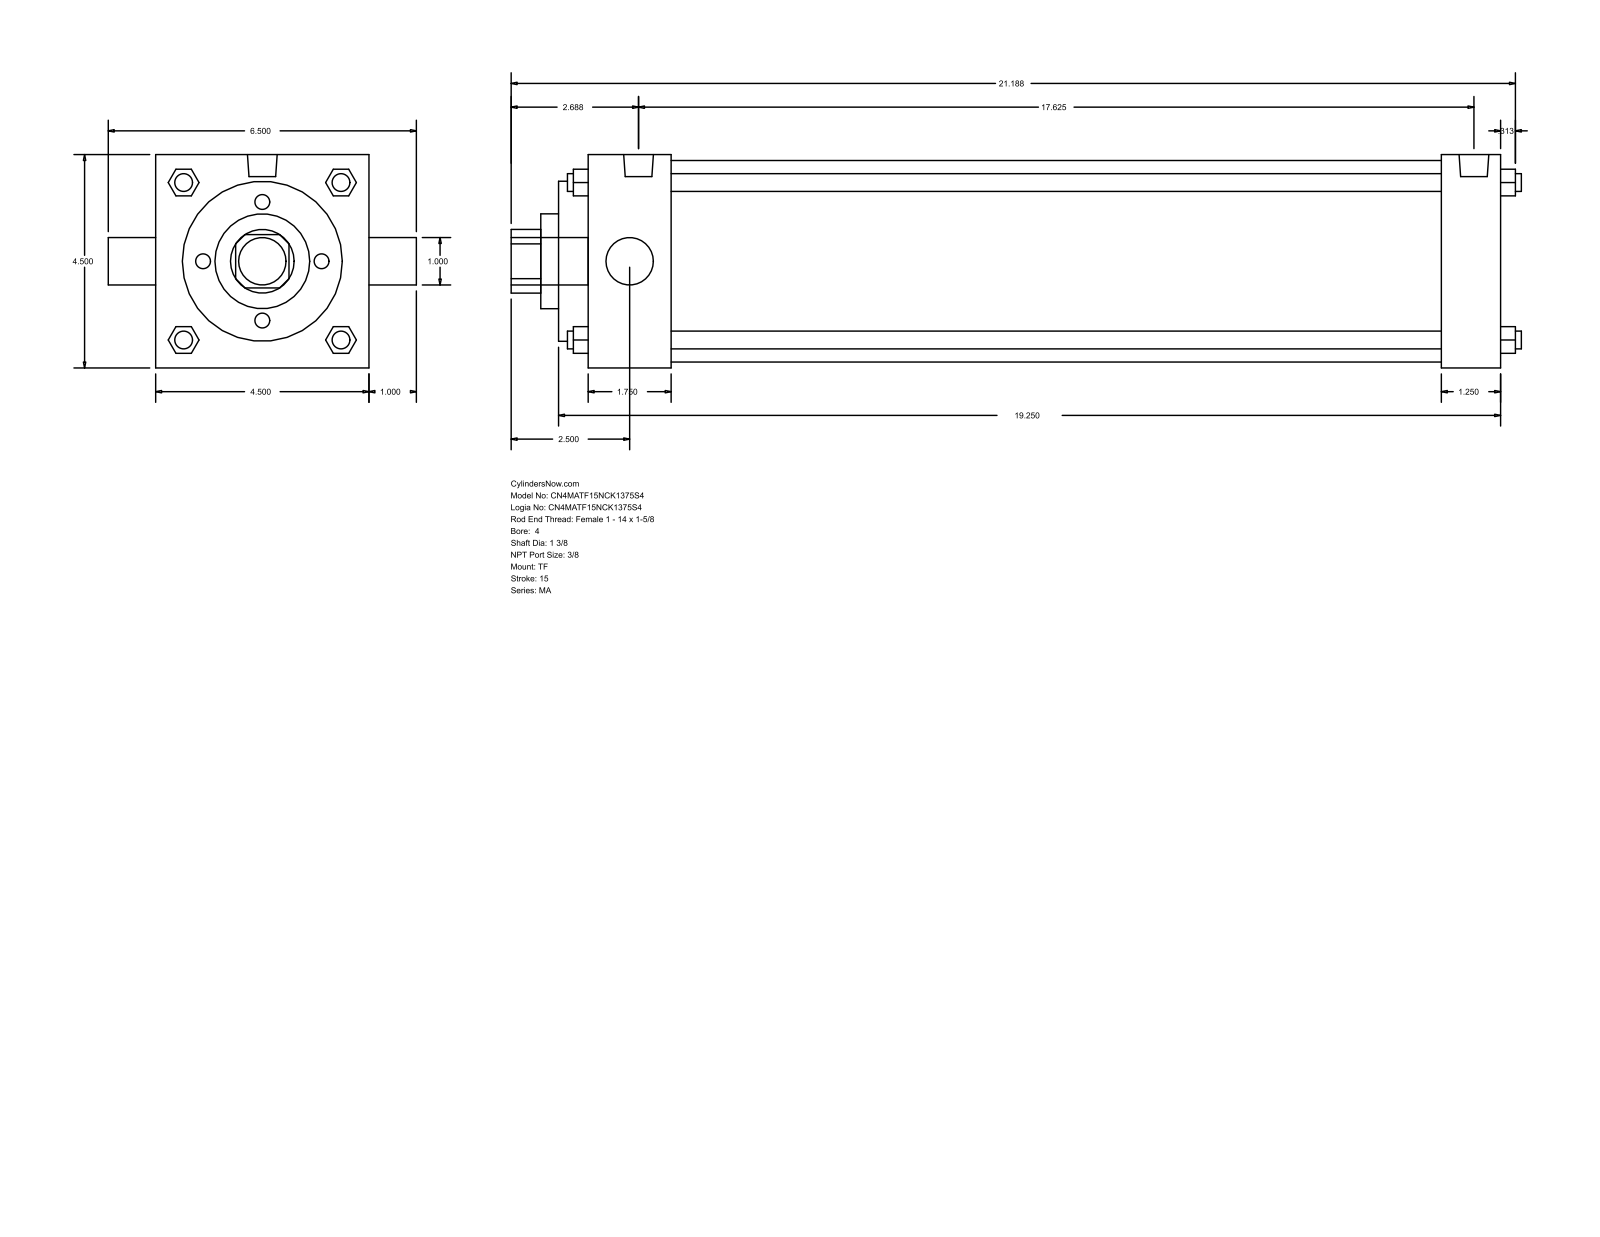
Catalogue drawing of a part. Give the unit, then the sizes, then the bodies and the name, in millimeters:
Units: millimetres
Overall size (bounding box): 541.34 × 165.1 × 114.3
Round holes (diameter × count): ⌀25.4 ×1, ⌀34.92 ×1, ⌀50.8 ×1, ⌀85.72 ×1, ⌀107.95 ×1
Round bosses / shafts (diameter × count): ⌀9.53 ×4, ⌀11.11 ×3, ⌀15.93 ×2, ⌀25.4 ×1
Partial cylindrical surfaces — rounded edges, fillets, slot ends (radius × count): R17.06 ×1
Main face-to-face distances: 114.3, 488.96, 15.87, 504.83, 473.08, 457.21, 31.75, 60.32, 44.45, 412.76
Bodies: 0 solids, 122 faces (93 planar, 29 cylindrical, 0 other)
Part name (STEP PRODUCT): MA_TF__0400_1.375
STEP written by: GSSL Pune (CONFIG_CONTROL_DESIGN)
